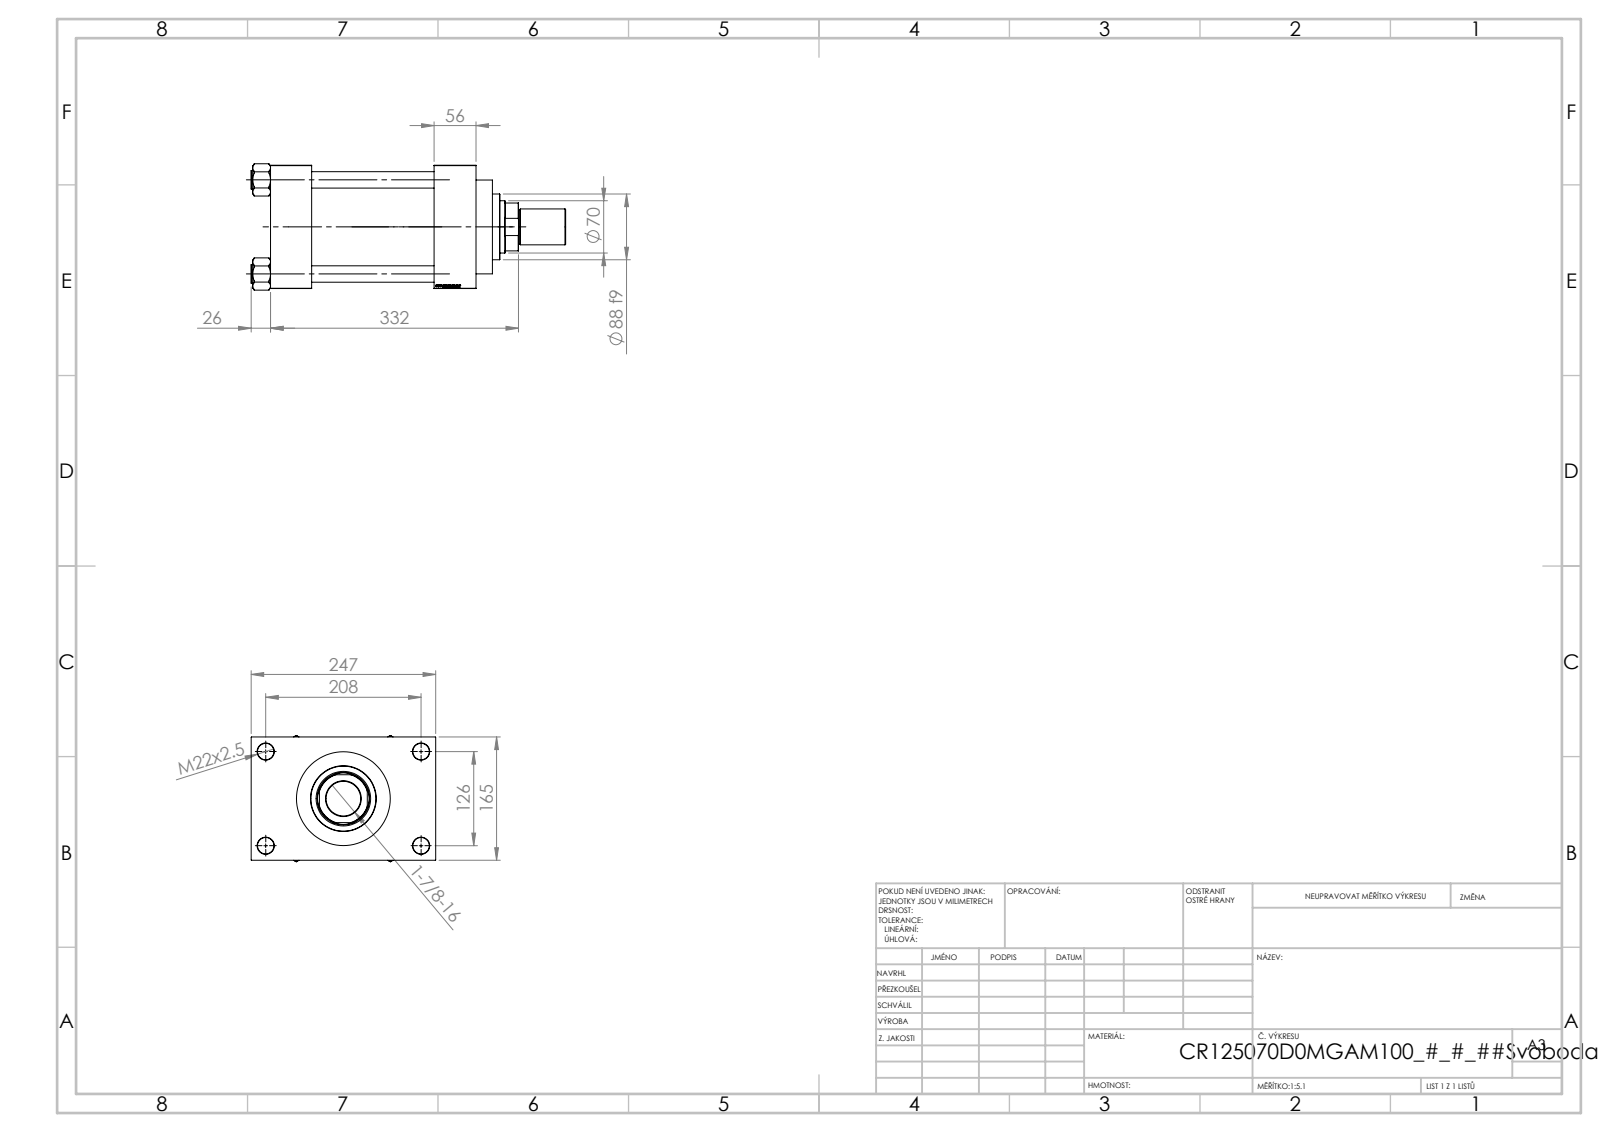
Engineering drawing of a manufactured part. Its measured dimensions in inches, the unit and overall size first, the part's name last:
Units: inches
Overall size (bounding box): 16.575 × 9.724 × 6.659
Round holes (diameter × count): ⌀0.866 ×8, ⌀0.276 ×2, ⌀1.269 ×2, ⌀1.772 ×2, ⌀1.831 ×1, ⌀2.756 ×1, ⌀2.874 ×1, ⌀3.78 ×1, ⌀4.921 ×1, ⌀4.941 ×1
Round bosses / shafts (diameter × count): ⌀0.984 ×4, ⌀5.157 ×1, ⌀3.465 ×1, ⌀1.89 ×1, ⌀1.811 ×1
Partial cylindrical surfaces — rounded edges, fillets, slot ends (radius × count): R1.339 ×1
Main face-to-face distances: 6.457, 6.496, 2.165, 8.622, 10.827, 8.661, 2.205, 1.614, 8.11, 9.99
Hole centre spacings: 1.616, 3.505, 4.787, 4.957, 5.215, 6.573, 8.233, 4.961
Volume: 347 in³ · Surface area: 1 016 in²
Bodies: 12 solids, 1163 faces (548 planar, 91 cylindrical, 524 other)
Part name (STEP PRODUCT): V215_VC_A; ROD_END_AH; V215CR_D_Body; V215CR_D_TYCINKA (+2 more)
STEP written by: SolidWorks 2019 (CONFIG_CONTROL_DESIGN)
